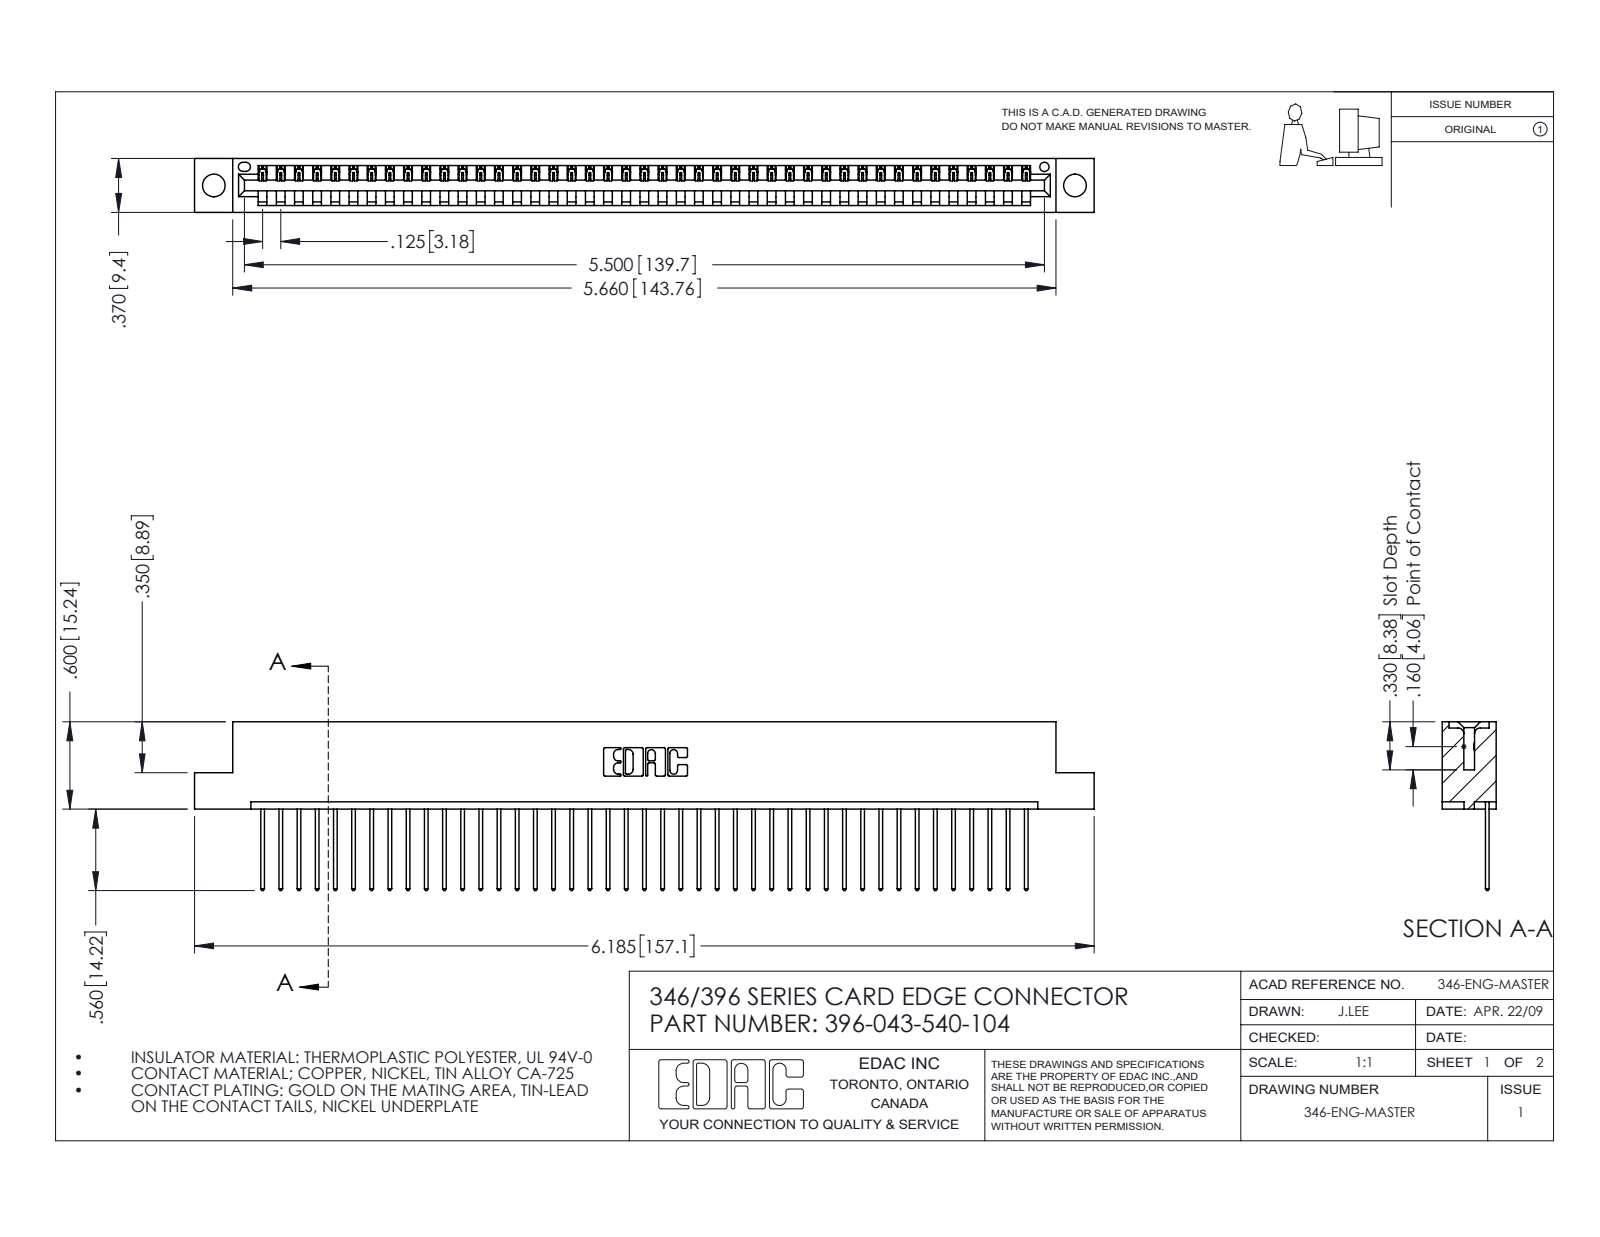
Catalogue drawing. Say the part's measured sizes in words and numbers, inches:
The part is named "346 Part_Flush Mounting Lugs - 0.156 Dia-TH; 345-292-001_345-293-140; 396-043-540-104". Its 3-D file was written by "SolidWorks 2016 (CONFIG_CONTROL_DESIGN)". It is 44 solids with 2616 faces: 1796 planar, 820 cylindrical and 0 other. Overall it measures 6.185 by 1.16 by 0.37 inches. Its volume is 0.916 cubic inches and its surface area 29.46 square inches. Round holes: 2 of diameter 0.156, 1 of diameter 0.064. Partial cylindrical surfaces (rounded edges, fillets, slot ends): 86 of radius 0.006, 86 of radius 0.01, 22 of radius 0.01, 6 of radius 0.007, 6 of radius 0.031, 3 of radius 0.026, 2 of radius 0.031, 2 of radius 0.04. The main face-to-face distances are 0.048, 0.322, 0.37, 0.25, 0.072, 0.298, 0.025, 0.148, 0.222, 0.1. The hole center spacings are 0.246, 5.711, 5.92.
